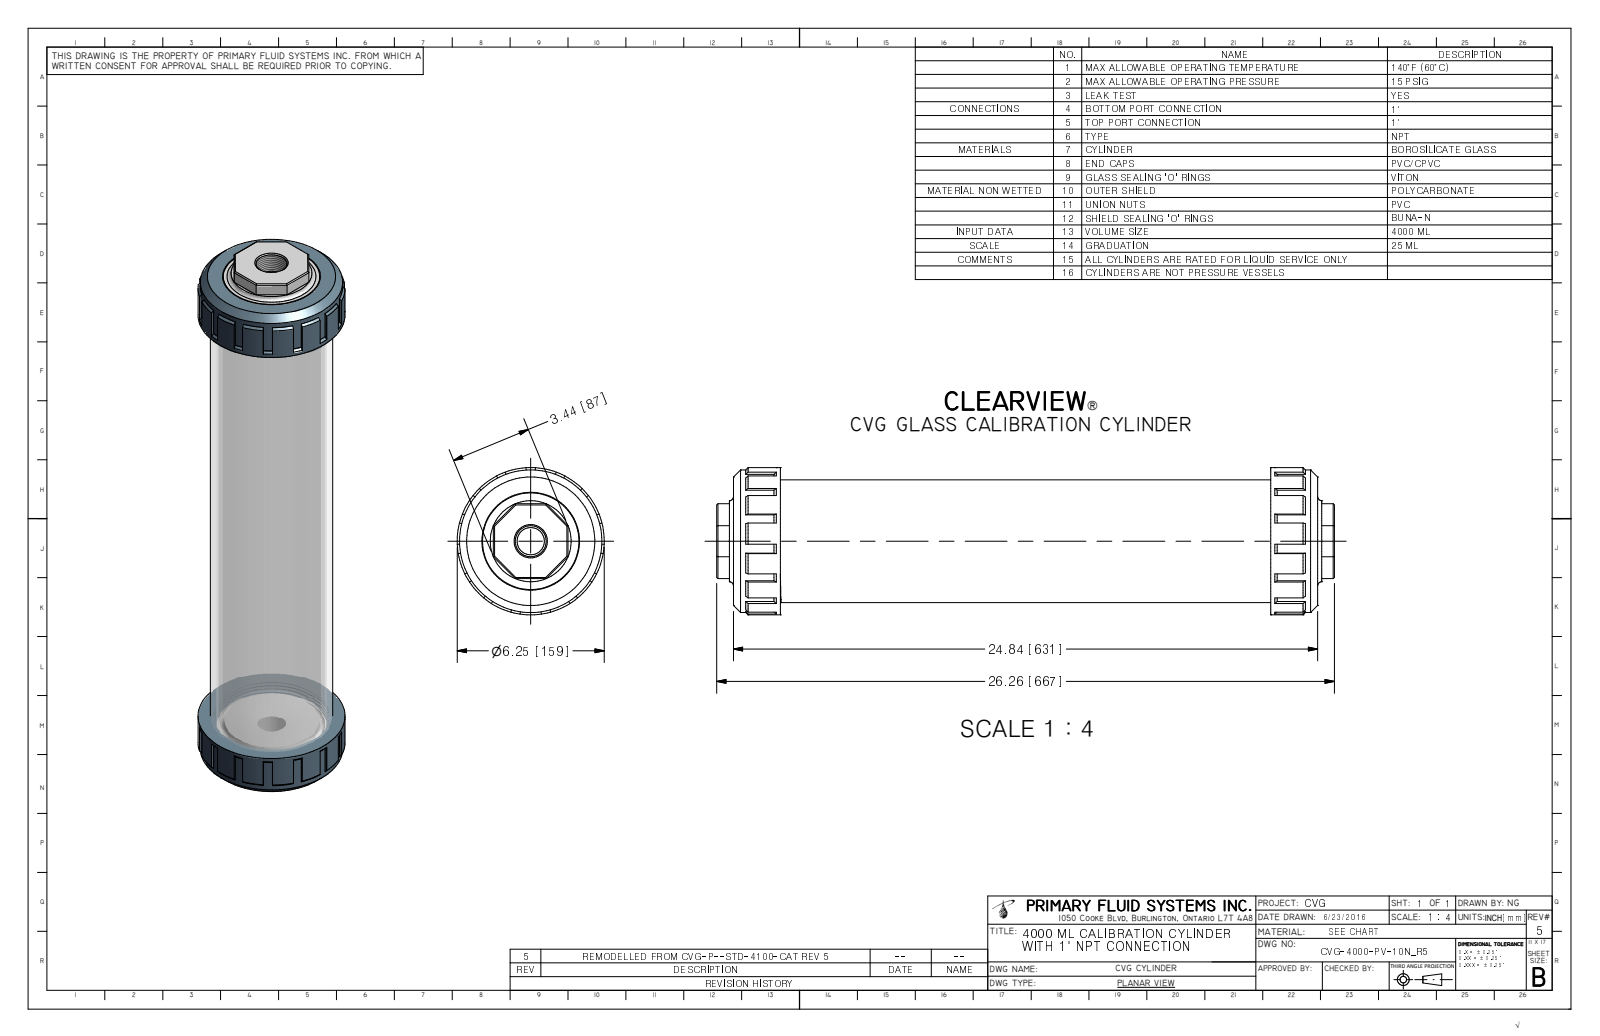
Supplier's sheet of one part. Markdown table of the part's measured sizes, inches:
| quantity | value |
| --- | --- |
| part name | CVG-4000-PVC-10N_R5; CVG-3-4000-POLY-NPT-10_R0; CVG-6-4000; CVG-1-4000-A_R0 (+1 more) |
| STEP written by | Autodesk Inventor 2009 (AUTOMOTIVE_DESIGN) |
| units | inches |
| bodies | 6 solids, 323 faces (110 planar, 71 cylindrical, 142 other) |
| overall size | 26.26 × 6.25 × 6.25 |
| volume | 251.3 in³ |
| surface area | 1 753 in² |
| round holes (diameter × count) | 1.156 × 1, 4.134 × 1, 4.15 × 1, 4.54 × 1, 4.682 × 1, 4.933 × 1, 5.201 × 1 |
| round bosses / shafts (diameter × count) | 6.25 × 1, 6.05 × 1, 4.893 × 1, 4.65 × 1, 4.528 × 1, 4.425 × 1, 4.1 × 1, 4.033 × 1 |
| main face-to-face distances | 2, 22.844, 0.5, 24.344, 1.5, 22.344, 0.708, 1.208, 2.708, 23.552 |
